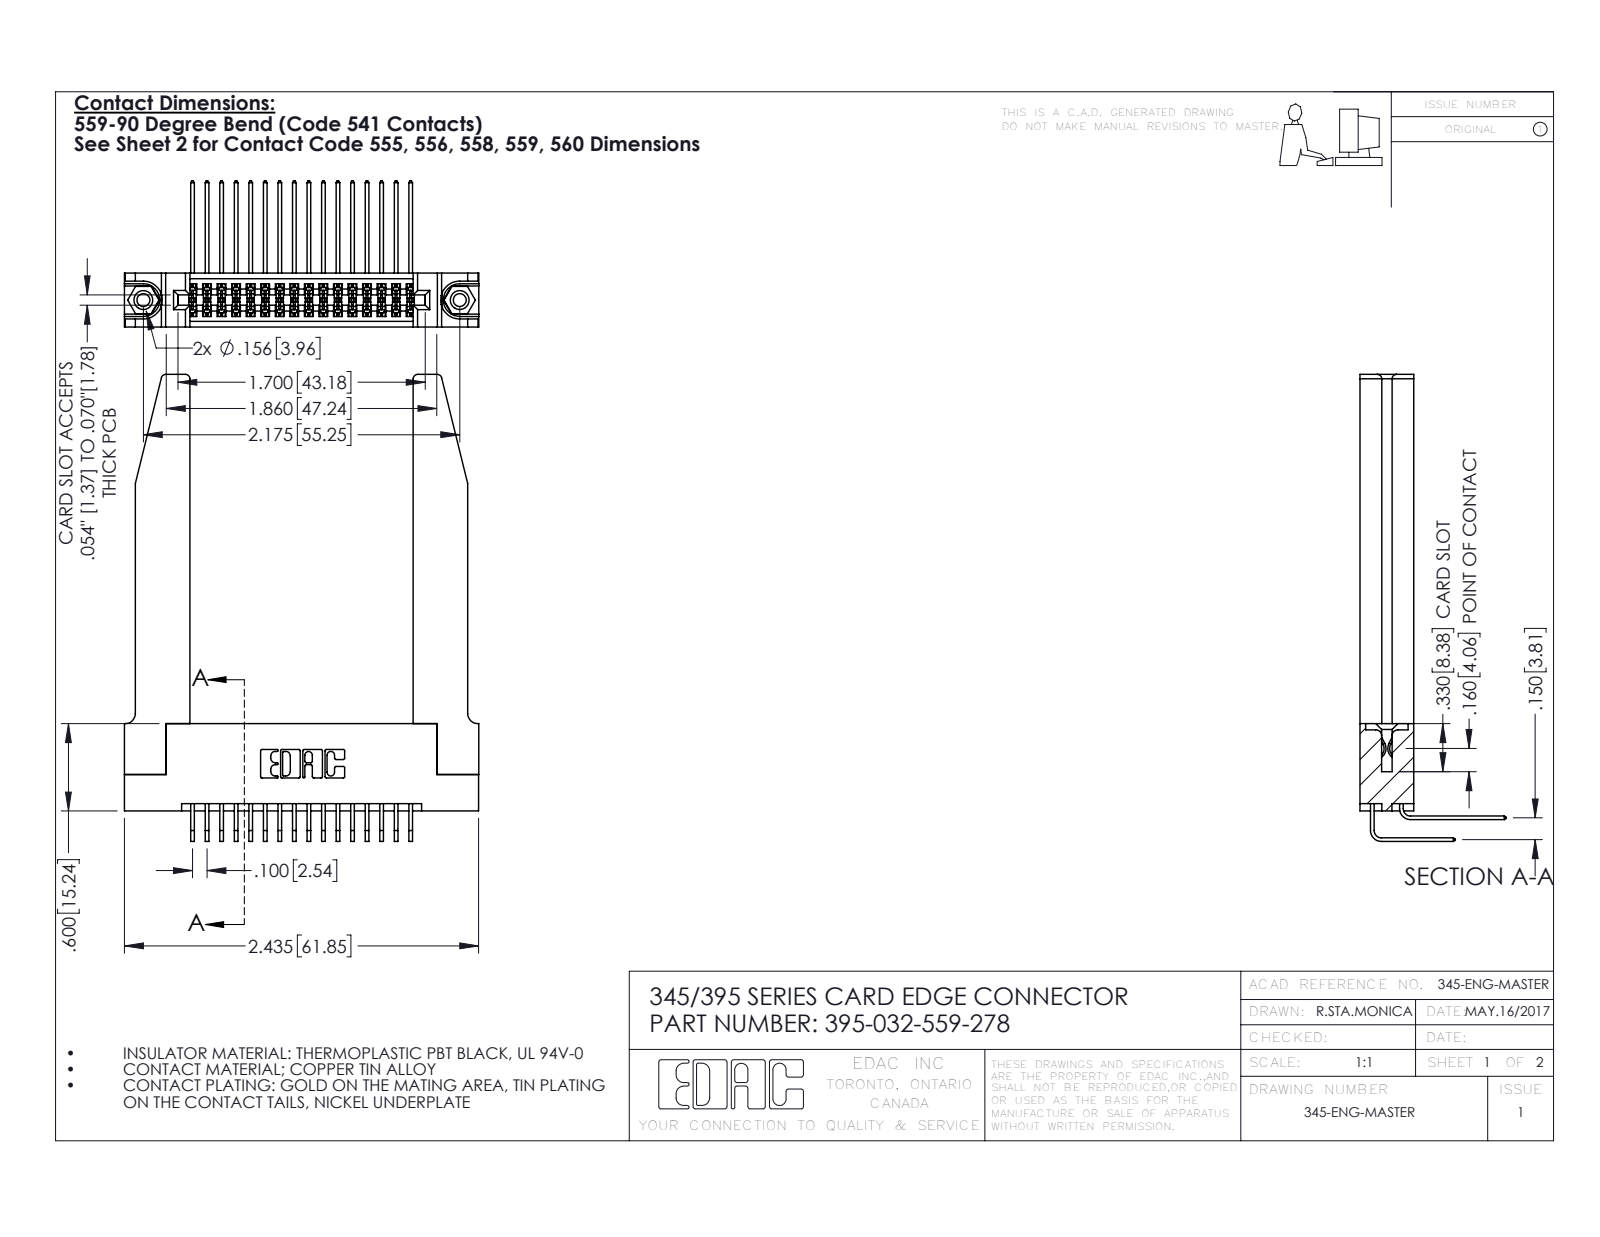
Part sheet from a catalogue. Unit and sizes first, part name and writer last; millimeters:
Units: millimetres
Overall size (bounding box): 81.5 × 61.9 × 25.5
Round holes (diameter × count): ⌀2.3 ×2, ⌀3.2 ×2, ⌀4 ×2, ⌀1.6 ×1
Round bosses / shafts (diameter × count): ⌀3.9 ×2
Partial cylindrical surfaces — rounded edges, fillets, slot ends (radius × count): R0.2 ×49, R0.3 ×22, R0.8 ×8, R0.2 ×6, R0.8 ×6, R0.7 ×3, R0.4 ×2, R0.5 ×2
Main face-to-face distances: 9.4, 1.8, 7.6, 5.1, 3.8, 3.8, 2.5, 6.9, 0.6, 2
Hole centre spacings: 6.9, 49.3, 55.2
Volume: 13 700 mm³ · Surface area: 16 010 mm²
Bodies: 37 solids, 2024 faces (1342 planar, 630 cylindrical, 52 other)
Part name (STEP PRODUCT): 345-292-001_559 Tail - 2; 345 Part_Flush Mounting Lugs - 0.156 Dia-TH; 345-250-001_345-250-001-102; 345-292-001_558 559 Tail - 1 (+2 more)
STEP written by: SolidWorks 2016 (CONFIG_CONTROL_DESIGN)
